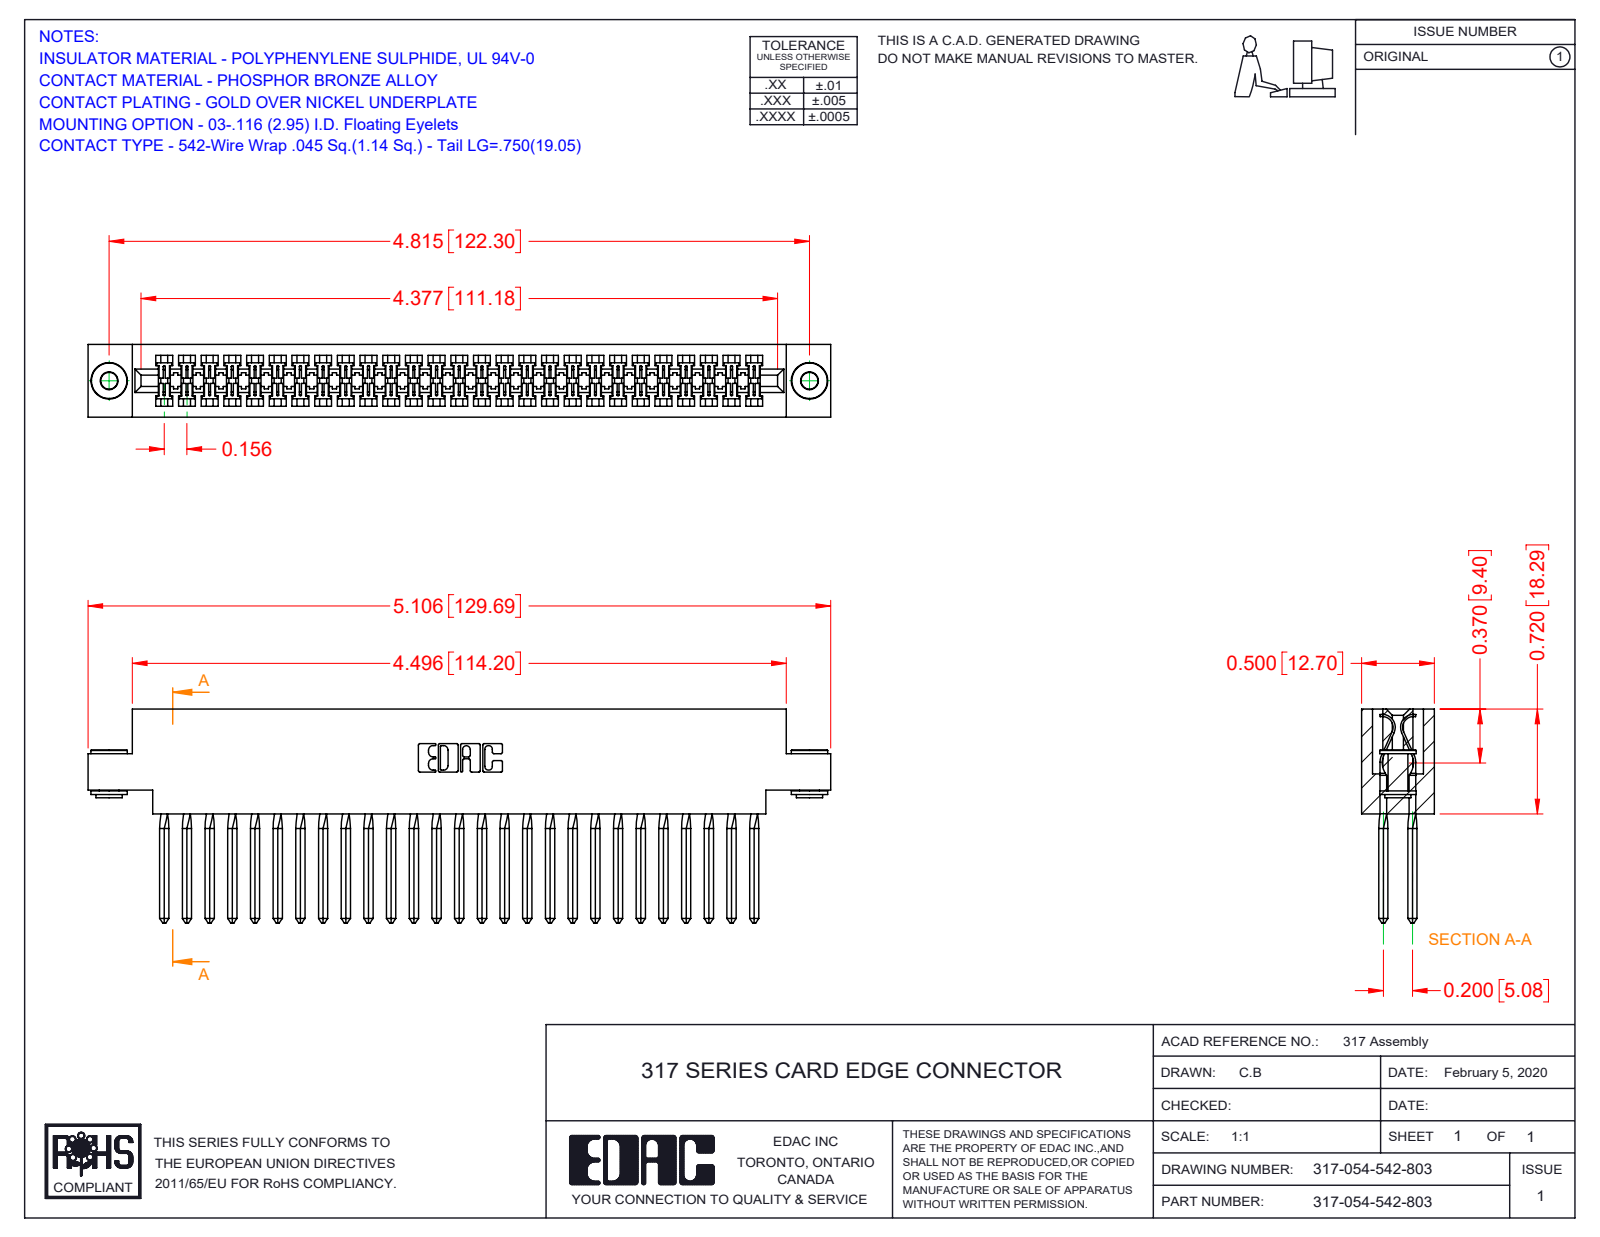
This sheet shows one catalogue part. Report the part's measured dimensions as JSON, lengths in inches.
{"part_name": "345-250-002_345-250-002-102; 317 Part_.156 Dia - TH; 317-290-003_542; 317-054-542-803", "step_written_by": "SolidWorks 2016 (CONFIG_CONTROL_DESIGN)", "units": "inches", "bodies": {"solids": 57, "faces": 3218, "planar": 2552, "cylindrical": 442, "other": 224}, "overall_size": [5.106, 1.47, 0.5], "volume_in3": 1.268, "surface_area_in2": 44.38, "round_holes": [[0.116, 2], [0.156, 2]], "round_bosses_or_shafts": [[0.25, 2], [0.18, 2], [0.136, 2]], "partial_cylinders_radius": [[0.006, 108], [0.01, 22], [0.007, 6], [0.031, 6], [0.026, 3], [0.074, 2], [0.089, 2], [0.1, 2]], "face_to_face_distances": [0.5, 0.075, 0.425, 0.35, 0.2, 0.11, 0.116, 0.046, 0.72, 0.128], "hole_center_spacings": [4.815]}
